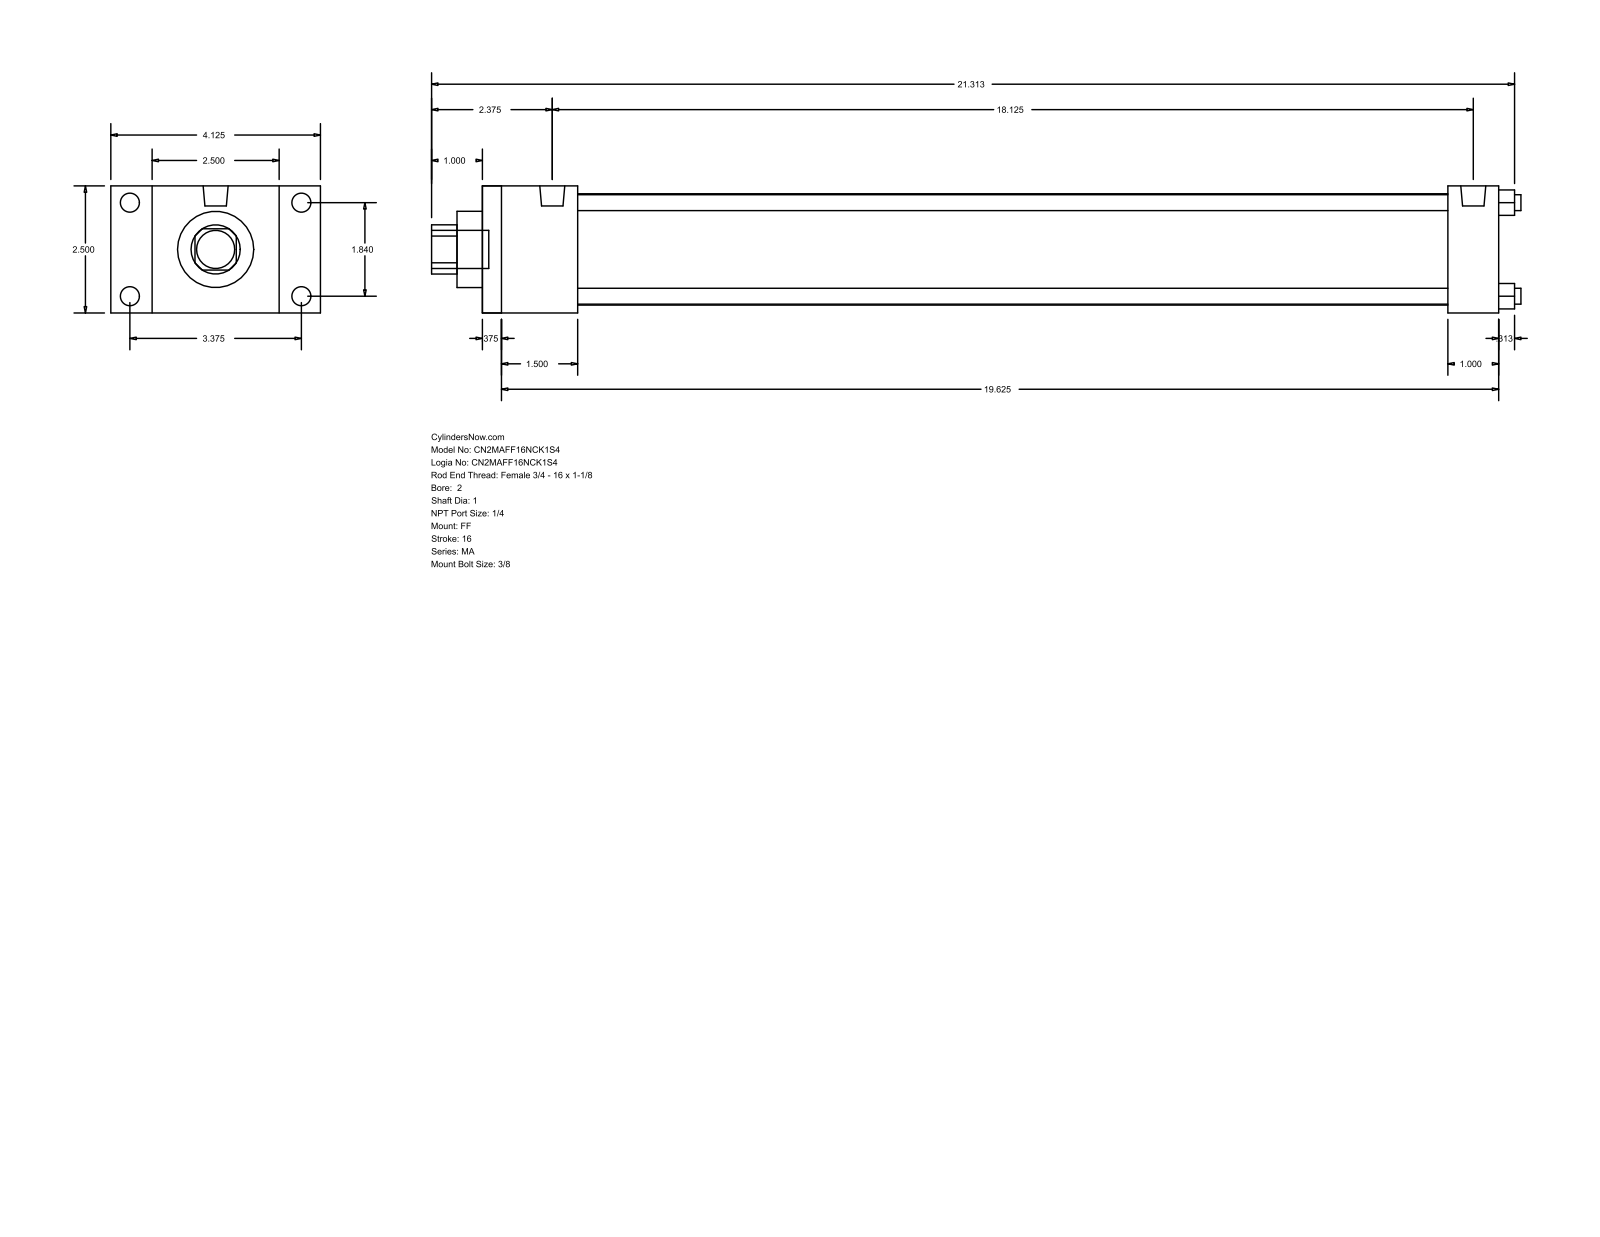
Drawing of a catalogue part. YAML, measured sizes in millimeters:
part_name: "MA_FF__0200_1"
step_written_by: "GSSL Pune (CONFIG_CONTROL_DESIGN)"
units: millimeters
bodies: {solids: 0, faces: 92, planar: 64, cylindrical: 28, other: 0}
overall_size: [544.51, 104.78, 63.5]
round_holes:
  - {diameter: 7.94, count: 4}
  - {diameter: 25.4, count: 1}
  - {diameter: 38.1, count: 1}
  - {diameter: 55.63, count: 1}
round_bosses_or_shafts:
  - {diameter: 9.53, count: 4}
  - {diameter: 7.94, count: 4}
  - {diameter: 12.49, count: 2}
  - {diameter: 19.05, count: 1}
partial_cylinders:
  - {radius: 12.29, count: 1}
face_to_face_distances: [63.5, 508, 9.52, 498.48, 25.4, 20.64, 12.7, 47.63, 482.6, 38.11]
hole_center_spacings: [33.05, 46.74, 66.1]
